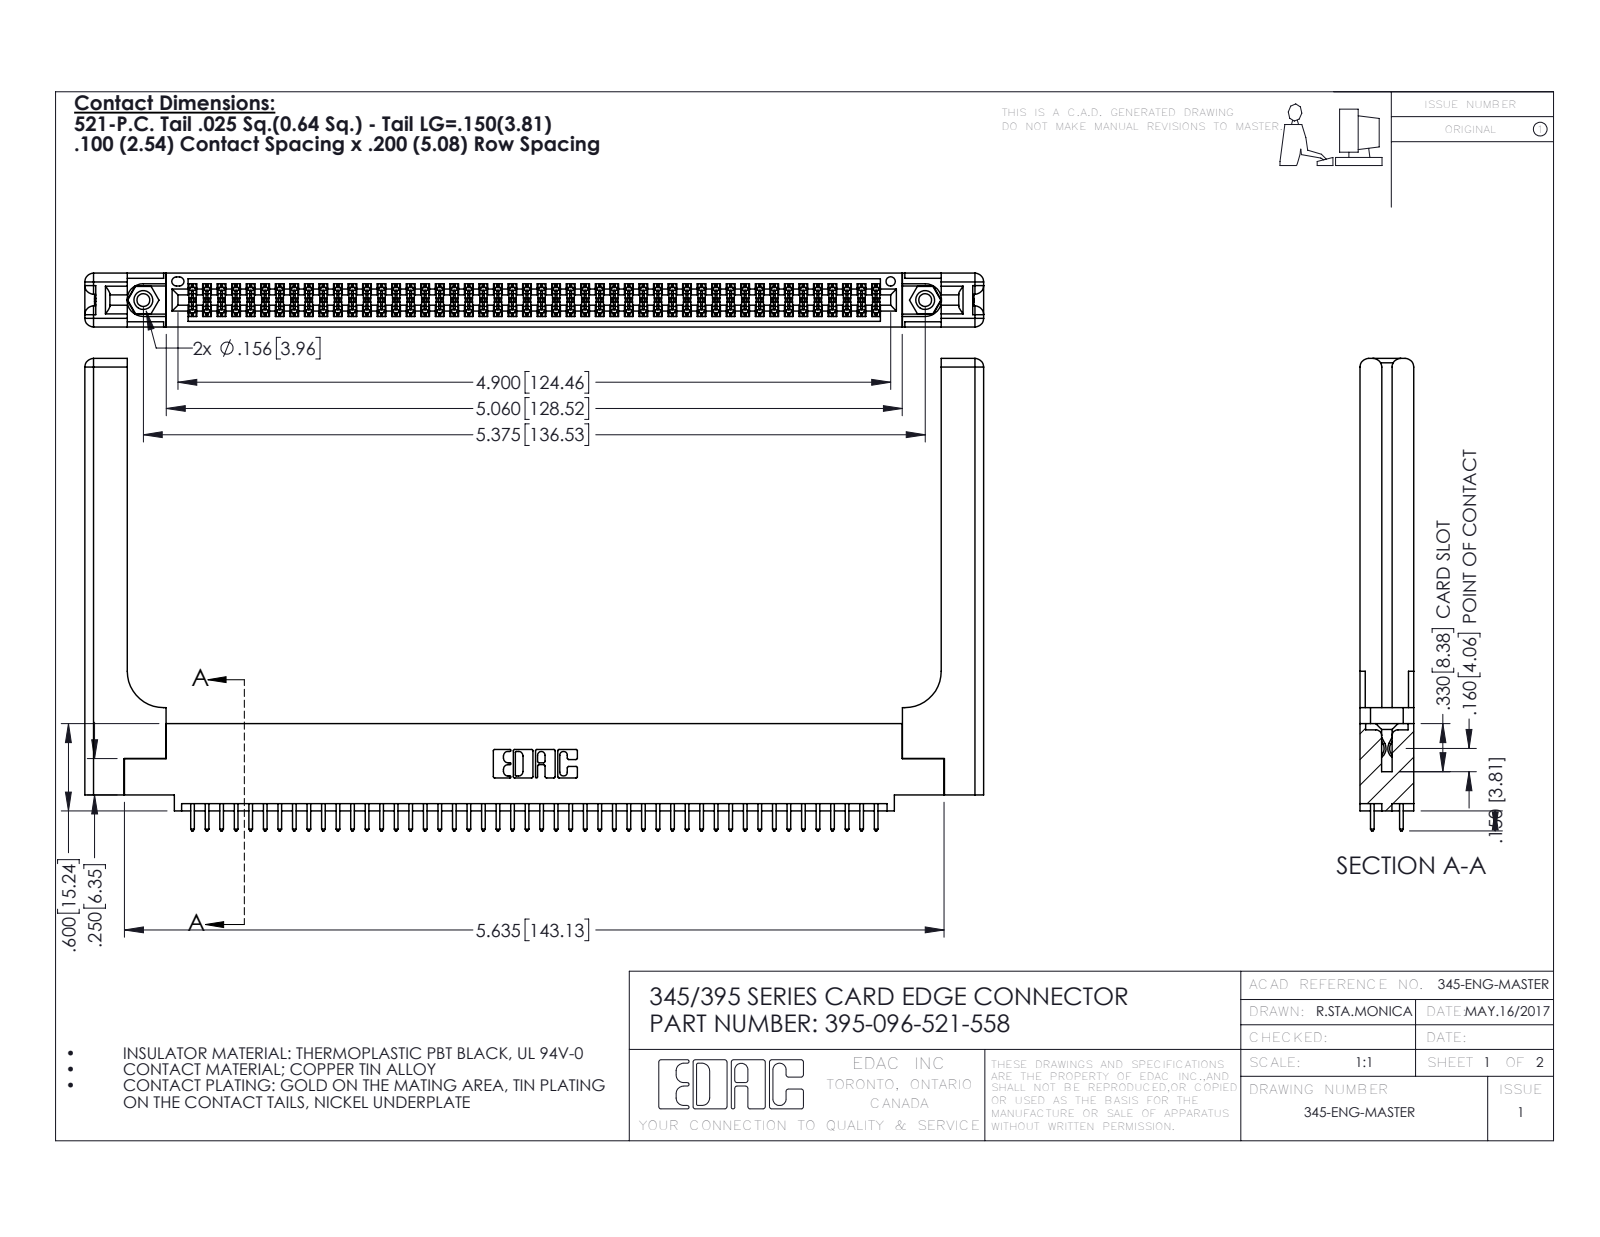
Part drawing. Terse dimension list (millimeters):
name: 345 Part_0.110 Offset - 0.156 Dia-TH; 345-292-001_345-293-121; 345-250-001_345-250-001-102; 345-220-058_345-220-058 (+1 more)
written by: SolidWorks 2016 (CONFIG_CONTROL_DESIGN)
unit: mm
bodies: 101 solids, 5186 faces (3400 planar, 1726 cylindrical, 60 other)
size: 156.9 × 82.5 × 9.4
volume: 23 660 mm³; area: 27 460 mm²
holes: 2× ⌀2.3, 2× ⌀3.2, 2× ⌀4, 1× ⌀1.6
bosses: 2× ⌀3.9
rounds: 144× R0.2, 96× R0.3, 22× R0.3, 16× R1.5, 6× R0.2, 6× R0.8, 3× R0.7, 2× R0.4
face distances: 1.8, 7.6, 9.4, 2.5, 6.9, 0.6, 5.1, 5.7, 3.8, 3.8
hole spacings: 6.9, 130.5, 136.5
